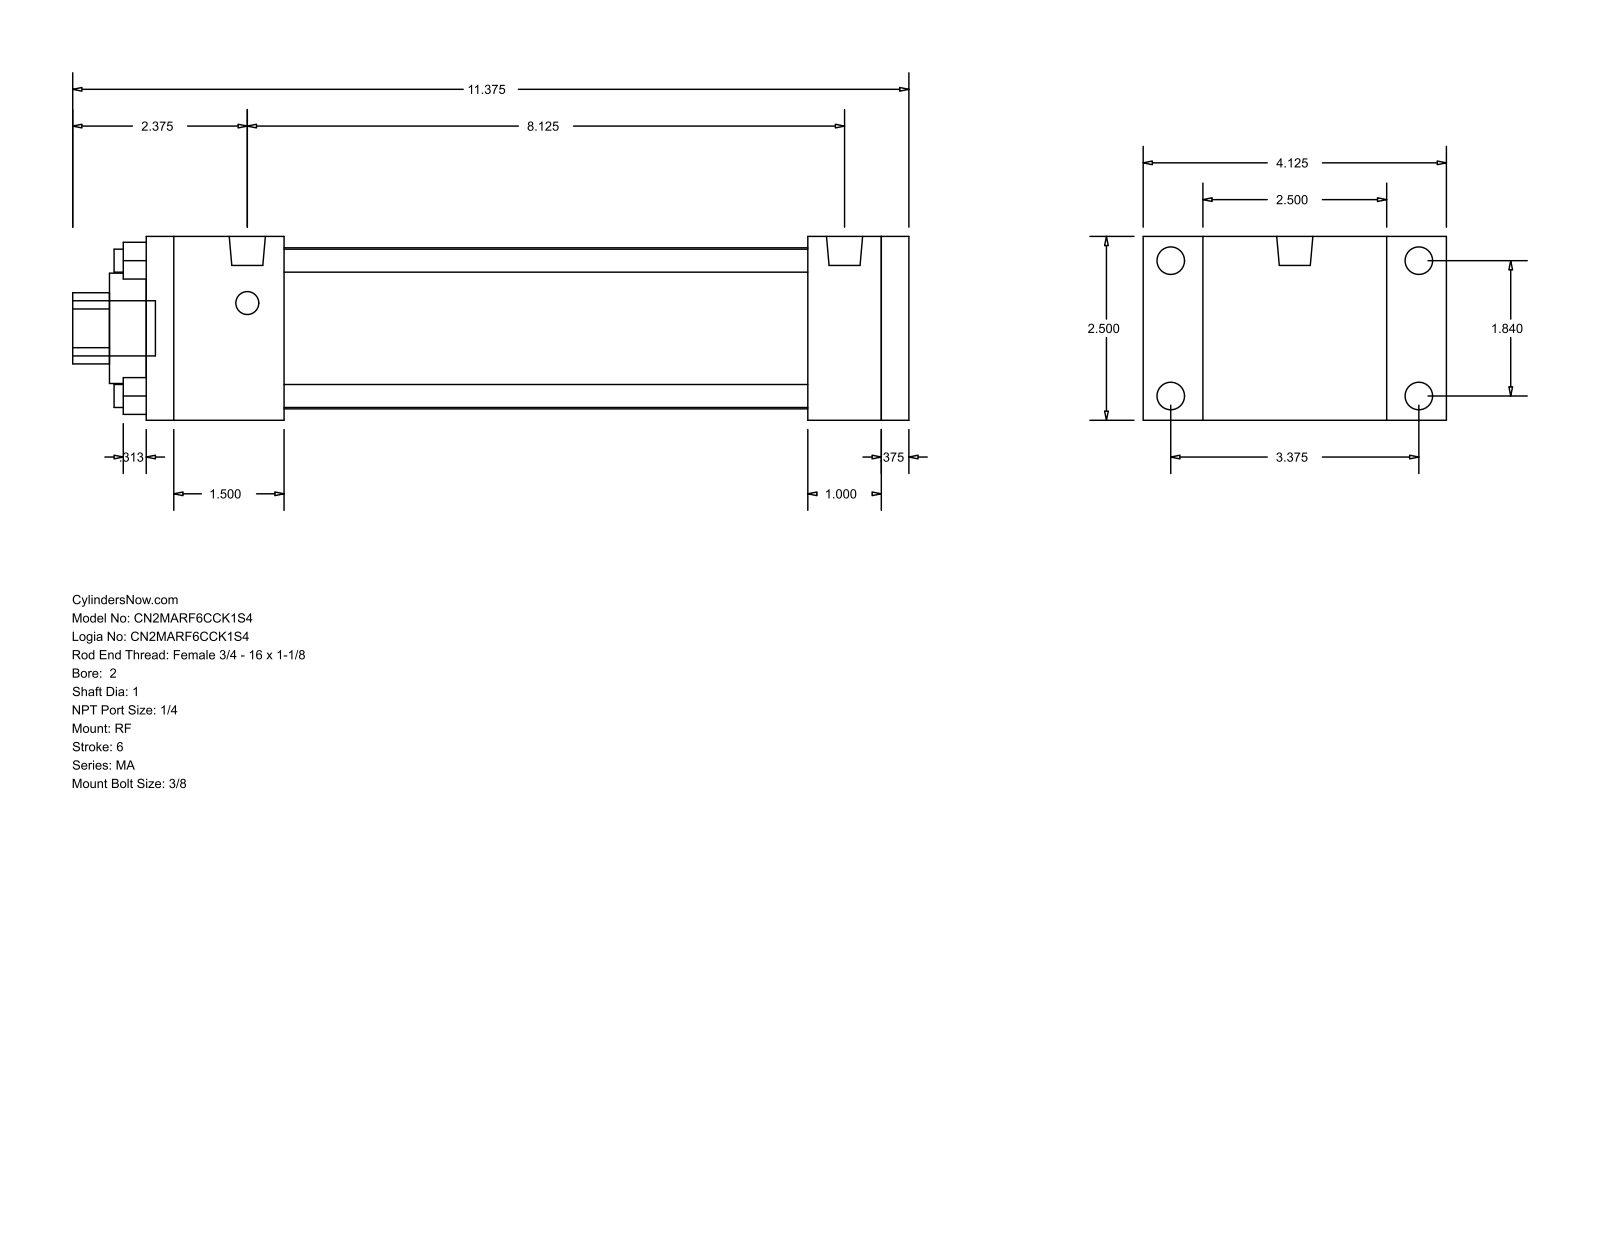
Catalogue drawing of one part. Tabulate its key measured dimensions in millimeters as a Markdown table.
| quantity | value |
| --- | --- |
| part name | MA_RF__0200_1 |
| STEP written by | GSSL Pune (CONFIG_CONTROL_DESIGN) |
| units | millimeters |
| bodies | 0 solids, 92 faces (64 planar, 28 cylindrical, 0 other) |
| overall size | 288.93 × 104.78 × 63.5 |
| round holes (diameter × count) | 7.94 × 4, 25.4 × 1, 38.1 × 1, 55.63 × 1 |
| round bosses / shafts (diameter × count) | 9.53 × 4, 7.94 × 4, 12.49 × 2, 19.05 × 1 |
| partial cylindrical surfaces (radius × count) | 12.29 × 1 |
| main face-to-face distances | 63.5, 254, 9.53, 263.53, 25.4, 20.64, 12.7, 47.63, 206.37, 215.9 |
| hole center spacings | 33.05, 46.74, 66.1 |
